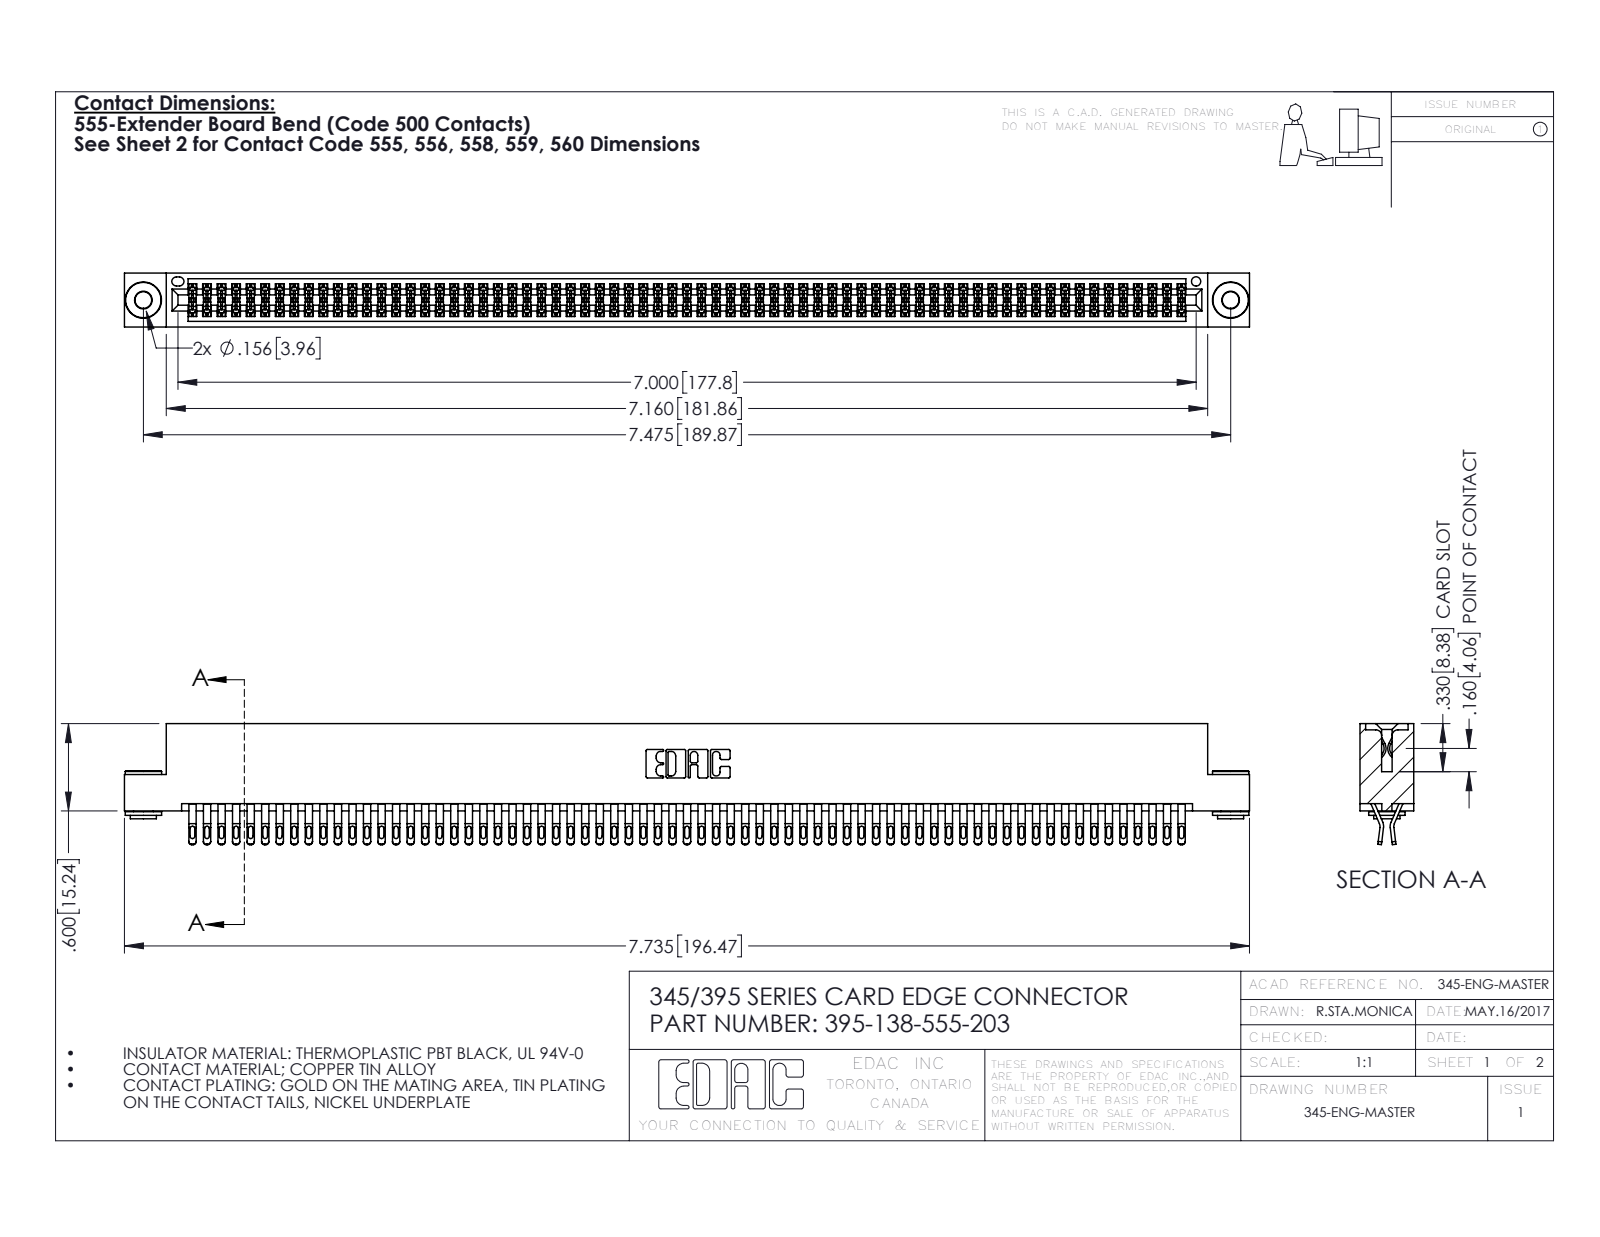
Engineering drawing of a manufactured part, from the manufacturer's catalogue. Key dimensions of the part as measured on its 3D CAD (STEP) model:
Part name (STEP PRODUCT): 345-292-001_555 Tail; 345-250-002_345-250-002-102; 345 Part_Flush Mounting Lugs - 0.156 Dia-TH; 395-138-555-203
STEP written by: SolidWorks 2016 (CONFIG_CONTROL_DESIGN)
Units: inches
Bodies: 141 solids, 7892 faces (4368 planar, 3516 cylindrical, 8 other)
Overall size (bounding box): 7.735 × 0.832 × 0.37
Volume: 1.206 in³ · Surface area: 48.55 in²
Round holes (diameter × count): ⌀0.116 ×2, ⌀0.156 ×2, ⌀0.064 ×1
Round bosses / shafts (diameter × count): ⌀0.25 ×2, ⌀0.18 ×2, ⌀0.136 ×2
Partial cylindrical surfaces — rounded edges, fillets, slot ends (radius × count): R0.016 ×345, R0.02 ×276, R0.006 ×207, R0.01 ×22, R0.007 ×6, R0.031 ×6, R0.026 ×3, R0.01 ×2
Main face-to-face distances: 0.072, 0.298, 0.025, 0.2, 0.37, 0.098, 0.272, 0.225, 0.175, 0.149
Hole centre spacings: 0.27, 7.239, 7.475
